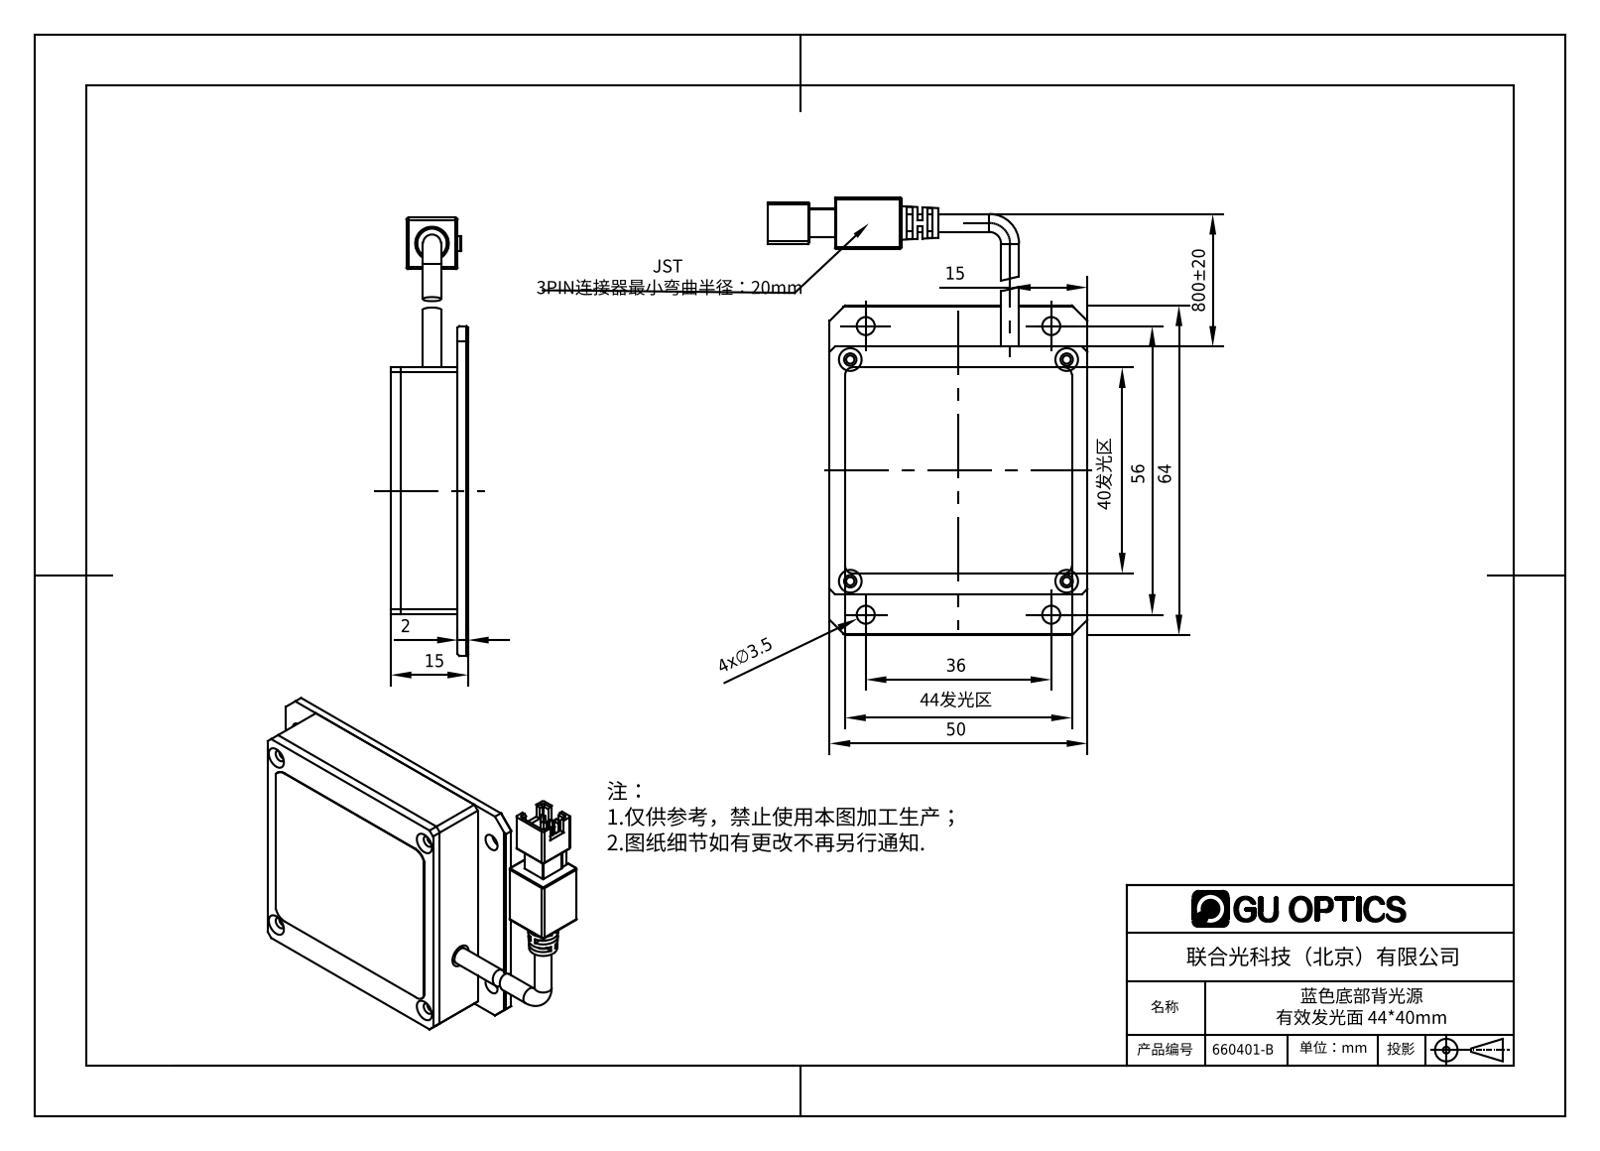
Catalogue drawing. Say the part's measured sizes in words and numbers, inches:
The part is named "660401-B". Its 3-D file was written by "SolidWorks 2016 (AUTOMOTIVE_DESIGN)". It is 6 solids with 476 faces: 239 planar, 118 cylindrical and 119 other. Overall it measures 3.346 by 2.441 by 0.594 inches. Its volume is 1.326 cubic inches and its surface area 36.46 square inches. Round holes: 8 of diameter 0.063, 8 of diameter 0.094, 4 of diameter 0.138. Round bosses or shafts: 2 of diameter 0.138. Partial cylindrical surfaces (rounded edges, fillets, slot ends): 15 of radius 0.004, 13 of radius 0.008, 12 of radius 0.016, 6 of radius 0.059, 4 of radius 0.039, 1 of radius 0.012, 1 of radius 0.027, 1 of radius 0.055. The main face-to-face distances are 0.079, 0.512, 0.433, 0.118, 0.039, 0.394, 0.083, 0.476, 0.594, 0.516. The hole center spacings are 0.039, 0.246, 0.282, 1.551, 1.557, 1.654, 1.654, 1.732.
